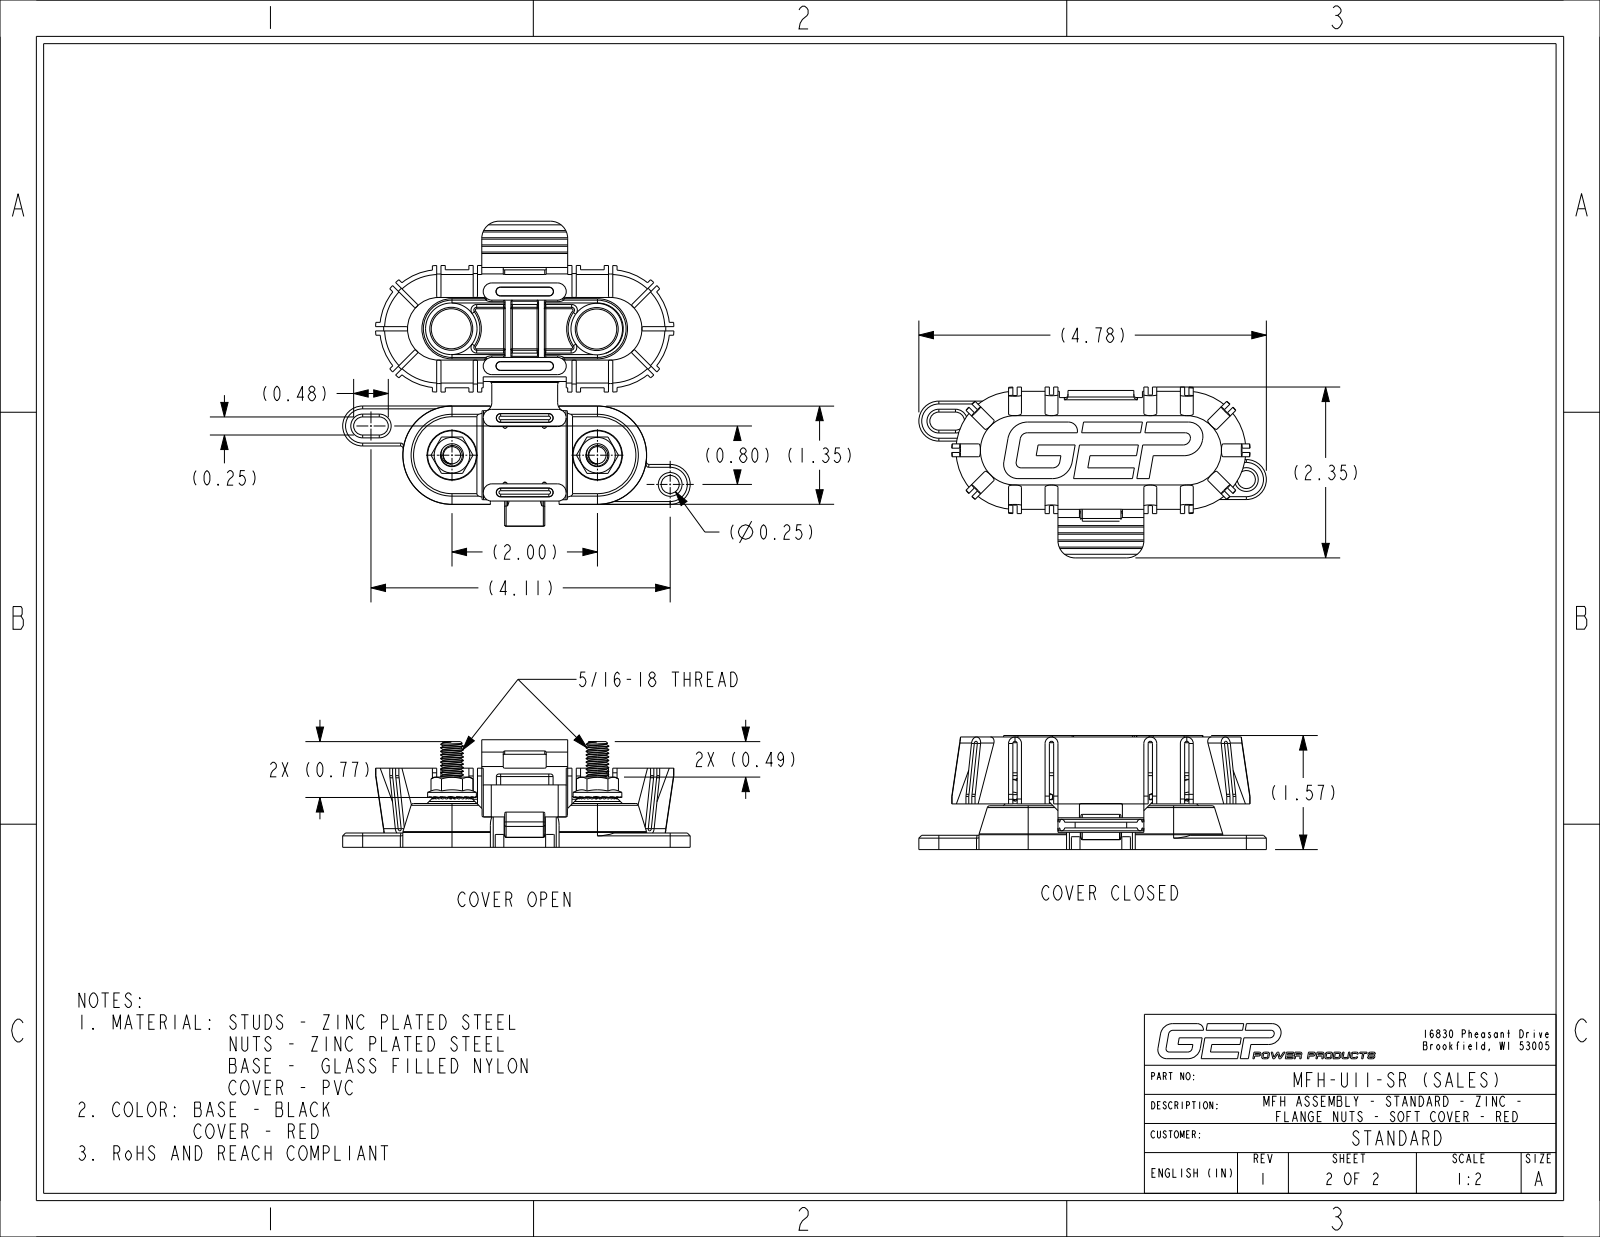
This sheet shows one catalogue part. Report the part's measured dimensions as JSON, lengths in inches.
{"part_name": "MFH-UXX-XX_BODY_NCF; C05-1003-U1_NCF; C02-1006-1_NCF; MFH-SR_NCF_INSTALLED (+1 more)", "step_written_by": "CREO PARAMETRIC BY PTC INC, 2024014 (CONFIG_CONTROL_DESIGN)", "units": "inches", "bodies": {"solids": 6, "faces": 2305, "planar": 893, "cylindrical": 747, "other": 665}, "overall_size": [4.778, 2.348, 1.568], "volume_in3": 3.275, "surface_area_in2": 86.64, "round_holes": [[0.244, 2], [0.354, 2], [0.591, 2], [0.248, 1]], "round_bosses_or_shafts": [[0.67, 2], [0.63, 2], [0.315, 2]], "partial_cylinders_radius": [[0.016, 236], [0.02, 24], [0.039, 20], [0.02, 14], [0.015, 13], [0.059, 12], [0.012, 10], [0.035, 10]], "face_to_face_distances": [0.059, 0.118, 0.079, 0.423, 0.177, 0.02, 0.6, 1.024, 0.482, 0.541], "hole_center_spacings": [2, 1.078, 1.088, 1.99, 2.01, 3.027, 3.037]}
